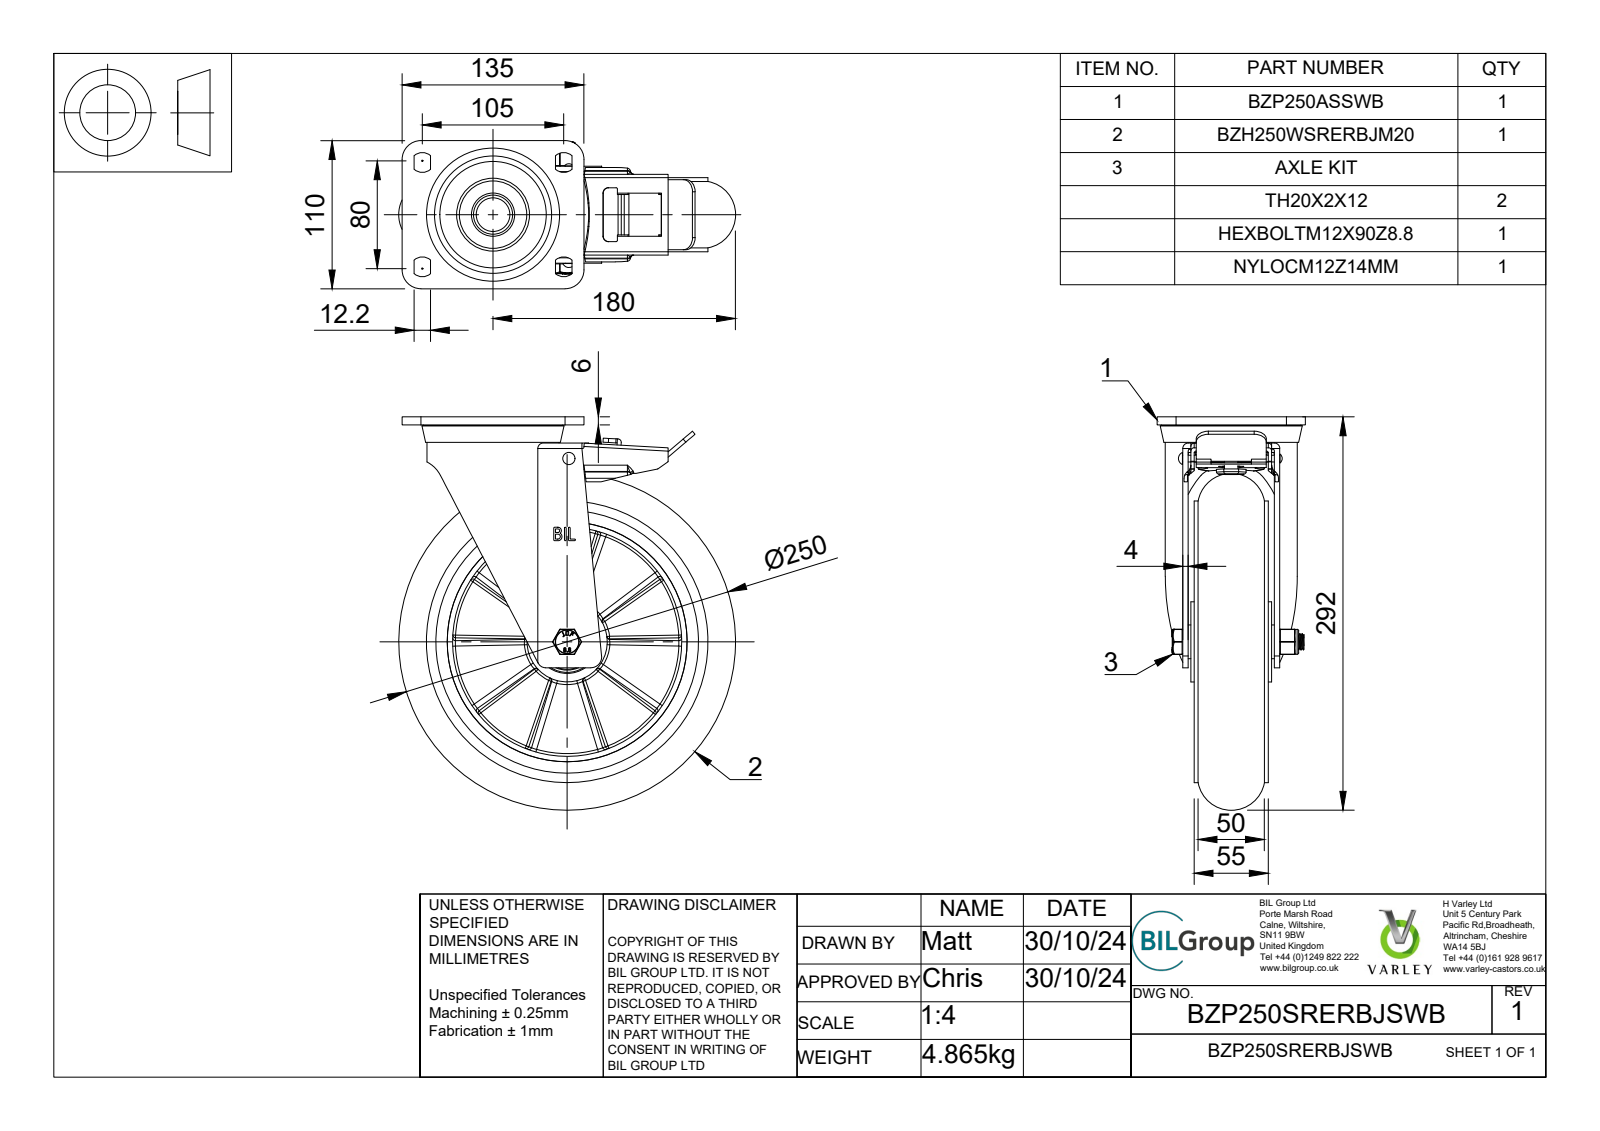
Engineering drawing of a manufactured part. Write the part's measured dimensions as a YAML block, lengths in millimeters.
part_name: "BZP250SRERBJSWB v4; BZP250ASSWB - 64 v1; ZINC PLATED, PRESSED STEEL TOP PLATE; ZINC PLATED, PRESSED STEEL TOP PLATE Geometry (+8 more)"
step_written_by: "Autodesk Translation Framework v13.20.0.188 (AUTOMOTIVE_DESIGN)"
units: millimeters
bodies: {solids: 43, faces: 1730, planar: 746, cylindrical: 311, other: 673}
overall_size: [292, 250, 110]
volume: 1776000
surface_area: 477515
round_holes:
  - {diameter: 5, count: 1}
  - {diameter: 10, count: 1}
  - {diameter: 12, count: 1}
  - {diameter: 12.2, count: 1}
  - {diameter: 14, count: 1}
  - {diameter: 19, count: 1}
  - {diameter: 20, count: 1}
  - {diameter: 28.5, count: 1}
  - {diameter: 30, count: 1}
  - {diameter: 30.8, count: 1}
  - {diameter: 40, count: 1}
  - {diameter: 40.3, count: 1}
round_bosses_or_shafts:
  - {diameter: 209, count: 1}
  - {diameter: 103.5, count: 1}
  - {diameter: 98, count: 1}
  - {diameter: 83, count: 1}
  - {diameter: 59.5, count: 1}
  - {diameter: 50, count: 1}
  - {diameter: 40.8, count: 1}
  - {diameter: 31.3, count: 1}
partial_cylinders:
  - {radius: 0.5, count: 20}
  - {radius: 1.5, count: 9}
  - {radius: 9.09, count: 8}
  - {radius: 1.25, count: 6}
  - {radius: 2.5, count: 6}
  - {radius: 4, count: 6}
  - {radius: 1, count: 5}
  - {radius: 2, count: 5}
face_to_face_distances: [4, 6, 17, 51, 55, 8.5, 2.5, 11, 7, 12.5]
hole_center_spacings: [136.03]
